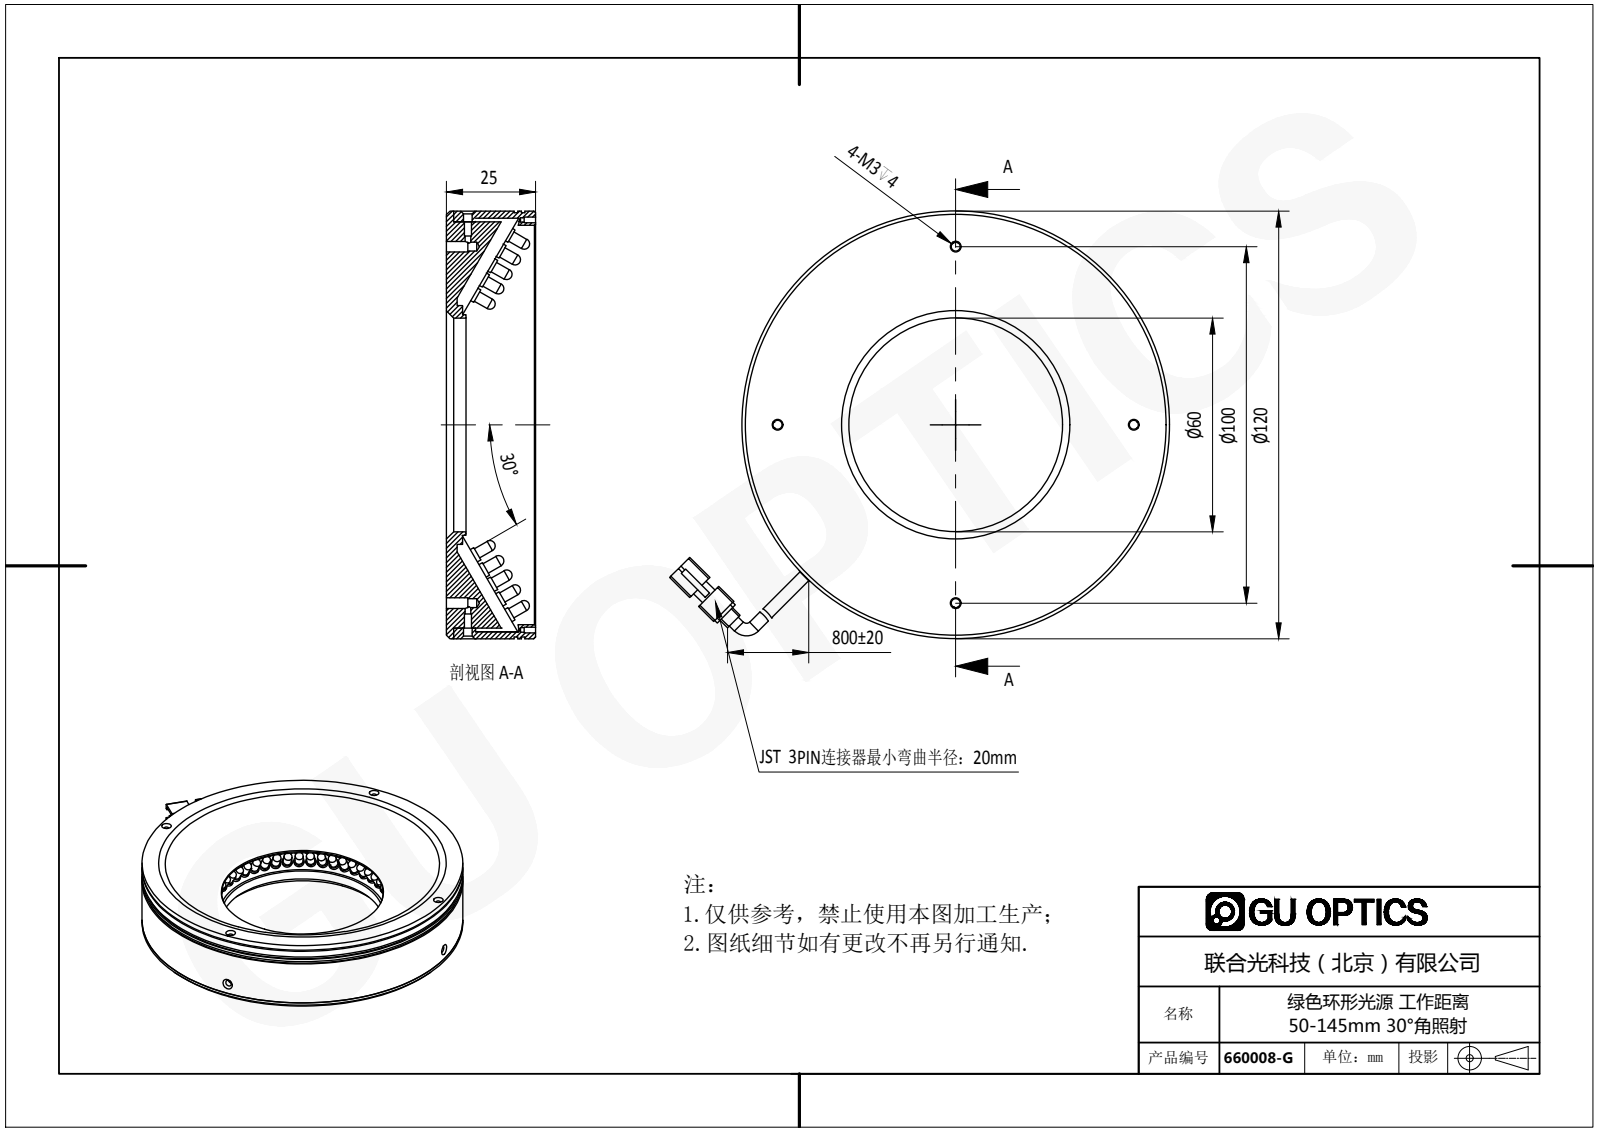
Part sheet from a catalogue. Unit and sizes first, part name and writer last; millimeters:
Units: millimetres
Overall size (bounding box): 140.26 × 120 × 29.45
Round holes (diameter × count): ⌀1.6 ×6, ⌀3.5 ×5, ⌀1.25 ×4, ⌀1.7 ×4, ⌀2.5 ×4, ⌀3 ×4, ⌀2 ×2, ⌀2.4 ×2, ⌀60 ×1, ⌀112 ×1, ⌀116 ×1
Round bosses / shafts (diameter × count): ⌀3.8 ×315, ⌀3 ×315, ⌀3.5 ×2, ⌀120 ×1, ⌀119 ×1, ⌀114 ×1, ⌀67 ×1, ⌀61.86 ×1
Partial cylindrical surfaces — rounded edges, fillets, slot ends (radius × count): R0.5 ×12, R1 ×4, R1.65 ×1, R8 ×1
Main face-to-face distances: 25, 2, 1, 23, 27, 0.5, 3, 2.5, 3.5, 20.15
Hole centre spacings: 76.2, 7.5, 50, 57.5, 70.71, 81.32, 107.5, 5.2
Volume: 123 170 mm³ · Surface area: 110 533 mm²
Bodies: 321 solids, 5663 faces (3870 planar, 1401 cylindrical, 392 other)
Part name (STEP PRODUCT): 660008-G
STEP written by: SolidWorks 2016 (AUTOMOTIVE_DESIGN)
